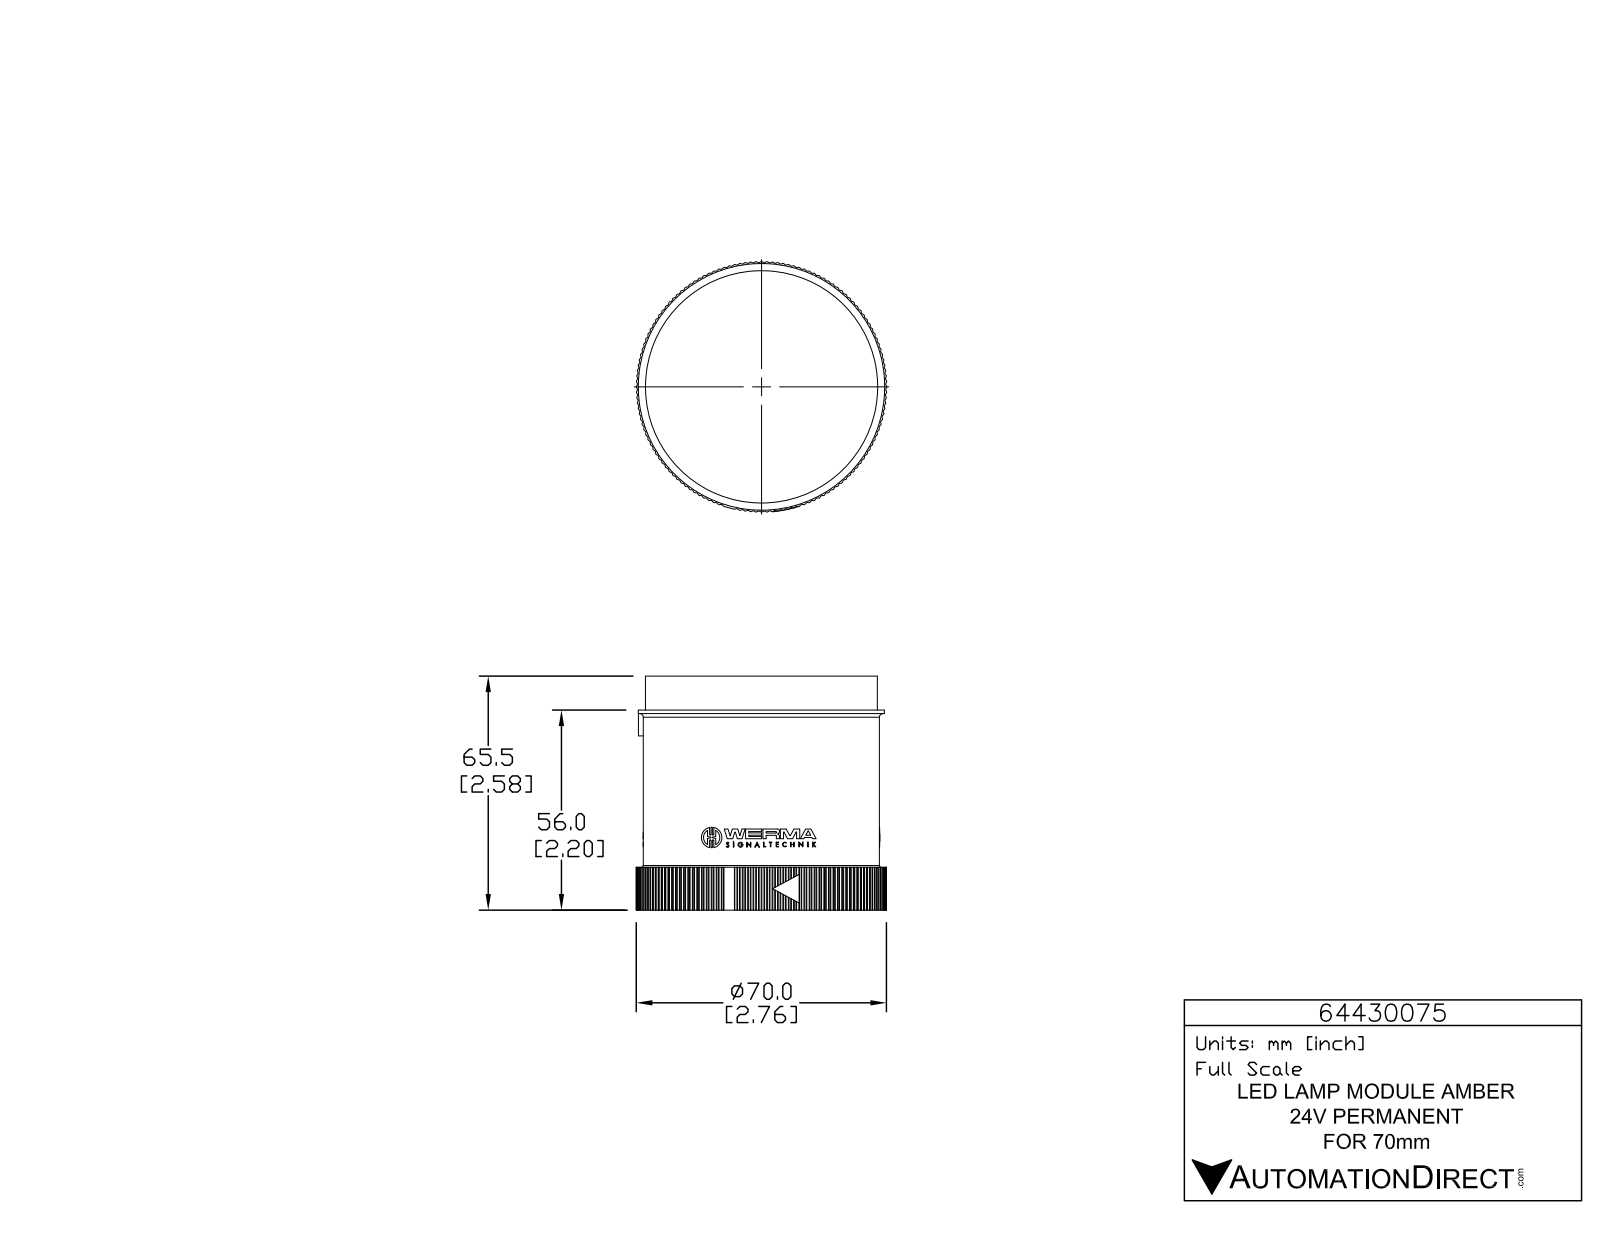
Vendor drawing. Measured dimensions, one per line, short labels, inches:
name: 64430075
written by: SolidWorks 2015 (AUTOMOTIVE_DESIGN)
unit: in
bodies: 1 solid, 1400 faces (832 planar, 563 cylindrical, 5 other)
size: 2.762 × 2.762 × 2.579
volume: 12.02 in³; area: 37.48 in²
holes: 3× ⌀0.039, 1× ⌀2.575
bosses: 3× ⌀0.226, 3× ⌀0.056, 1× ⌀2.717, 1× ⌀2.606, 1× ⌀2.559
rounds: 285× R0.008, 6× R0.008, 6× R0.008, 6× R0.008, 6× R0.131, 3× R0.004, 3× R0.005, 3× R0.008
face distances: 2.201, 2.451, 0.378, 2.579, 2.205, 1.827, 0.374, 2.452, 0.472, 0.094
